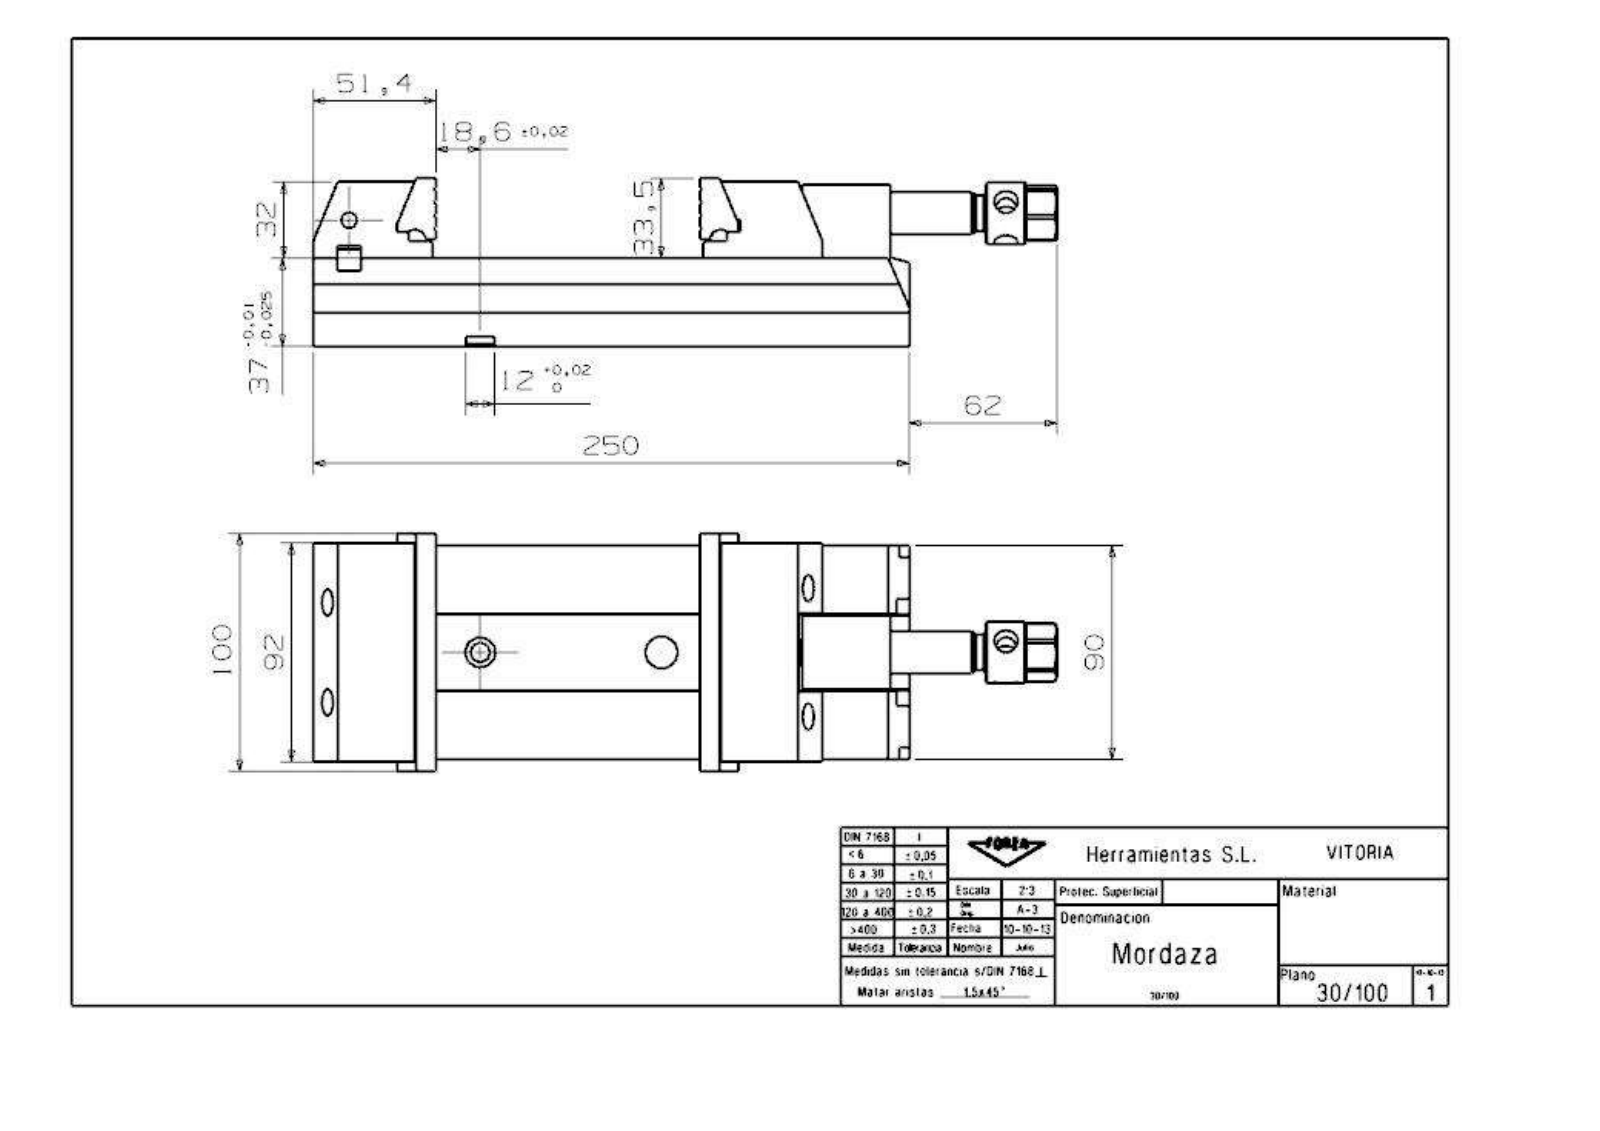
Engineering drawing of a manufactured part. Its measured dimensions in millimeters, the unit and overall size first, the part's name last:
Units: millimetres
Overall size (bounding box): 312 × 100 × 70.5
Round holes (diameter × count): ⌀4.35 ×5, ⌀6.99 ×5, ⌀13 ×5, ⌀5.19 ×4, ⌀6.5 ×4, ⌀7.5 ×4, ⌀11.5 ×4, ⌀8.4 ×2, ⌀8.5 ×2, ⌀10 ×2, ⌀10.58 ×2, ⌀13.5 ×2
Round bosses / shafts (diameter × count): ⌀26 ×1, ⌀17.73 ×1, ⌀15 ×1, ⌀14.5 ×1, ⌀10.5 ×1
Partial cylindrical surfaces — rounded edges, fillets, slot ends (radius × count): R0.4 ×16, R6 ×5, R7.5 ×4, R1.2 ×2, R5 ×2, R5.5 ×2, R2.5 ×1, R8 ×1
Main face-to-face distances: 37, 12.3, 5, 90, 13.4, 23.6, 22.5, 67.5, 40, 32
Hole centre spacings: 48, 6, 6.01, 42, 54, 11.07, 11.1, 13.12
Volume: 897 253 mm³ · Surface area: 193 781 mm²
Bodies: 11 solids, 397 faces (249 planar, 111 cylindrical, 37 other)
Part name (STEP PRODUCT): 30_100_Morzada
STEP written by: SIEMENS PLM Software NX 7.5 (AUTOMOTIVE_DESIGN)
